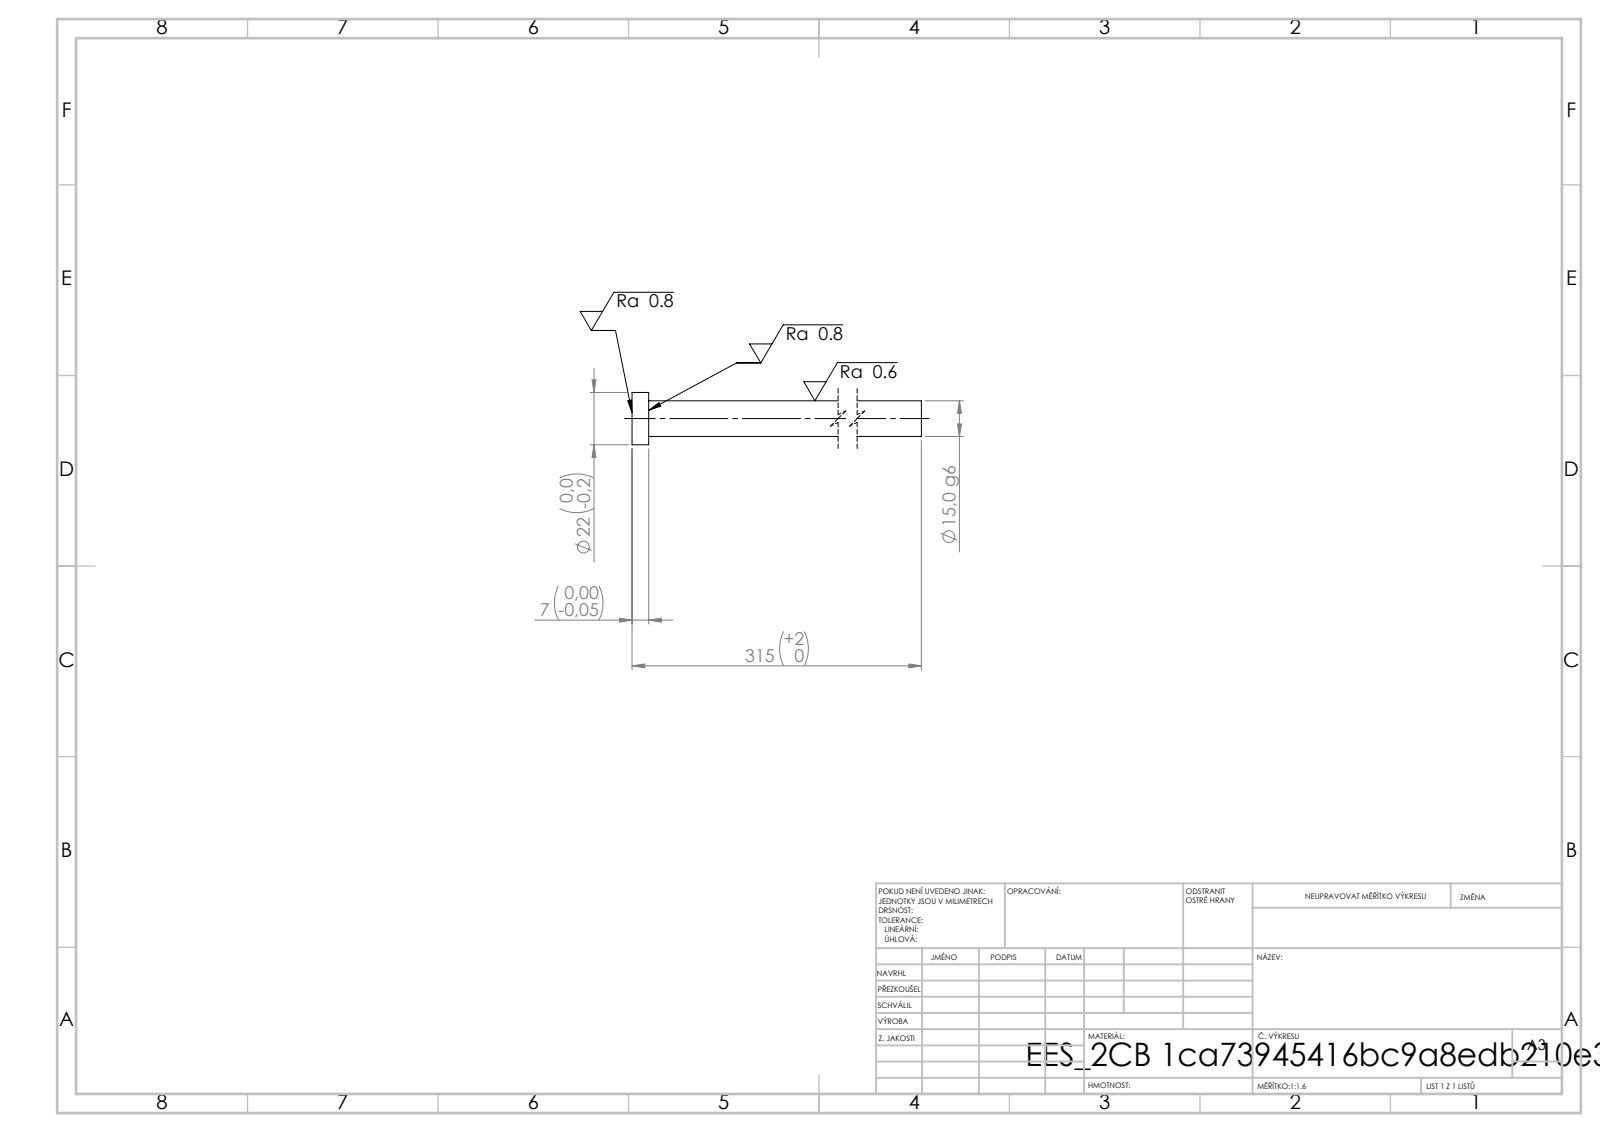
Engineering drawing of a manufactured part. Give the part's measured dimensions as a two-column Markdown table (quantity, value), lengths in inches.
| quantity | value |
| --- | --- |
| STEP written by | SolidWorks 2019 (CONFIG_CONTROL_DESIGN) |
| units | inches |
| bodies | 1 solid, 7 faces (3 planar, 4 cylindrical, 0 other) |
| overall size | 12.402 × 0.866 × 0.866 |
| volume | 3.484 in³ |
| surface area | 24.42 in² |
| round bosses / shafts (diameter × count) | 0.866 × 1, 0.591 × 1 |
| main face-to-face distances | 0.276, 12.402, 12.126 |
